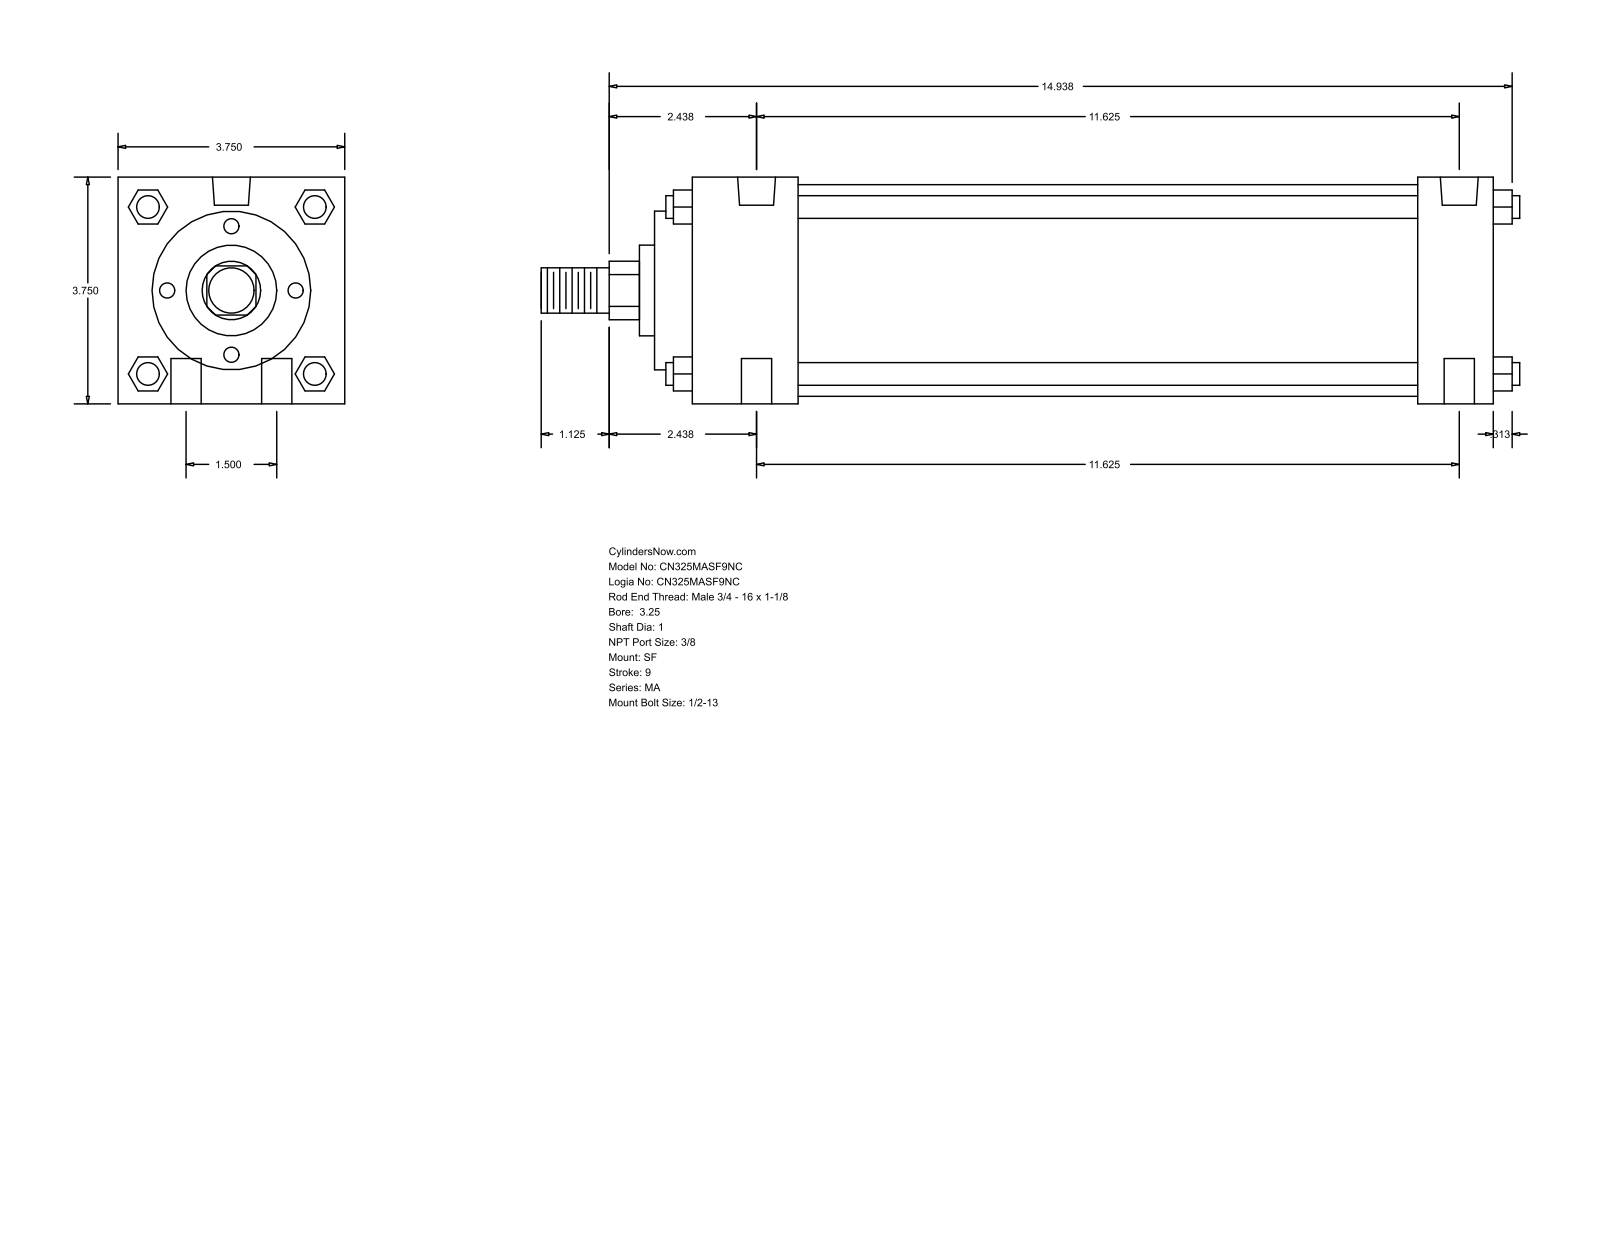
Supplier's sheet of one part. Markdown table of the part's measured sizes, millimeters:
| quantity | value |
| --- | --- |
| part name | MA_SF__0325_1 |
| STEP written by | GSSL Pune (CONFIG_CONTROL_DESIGN) |
| units | millimeters |
| bodies | 0 solids, 126 faces (95 planar, 31 cylindrical, 0 other) |
| overall size | 411.16 × 95.25 × 95.25 |
| round holes (diameter × count) | 12.7 × 4, 11.11 × 2, 15.93 × 2 |
| round bosses / shafts (diameter × count) | 9.53 × 4, 88.9 × 1, 66.67 × 1, 38.1 × 1, 25.4 × 1, 19.05 × 1 |
| partial cylindrical surfaces (radius × count) | 12.29 × 1 |
| main face-to-face distances | 95.24, 336.56, 304.81, 31.75, 44.46, 260.35, 292.1, 15.87, 60.33, 320.68 |
| hole center spacings | 19.05, 295.89, 295.28, 38.1, 297.73, 285.76 |
